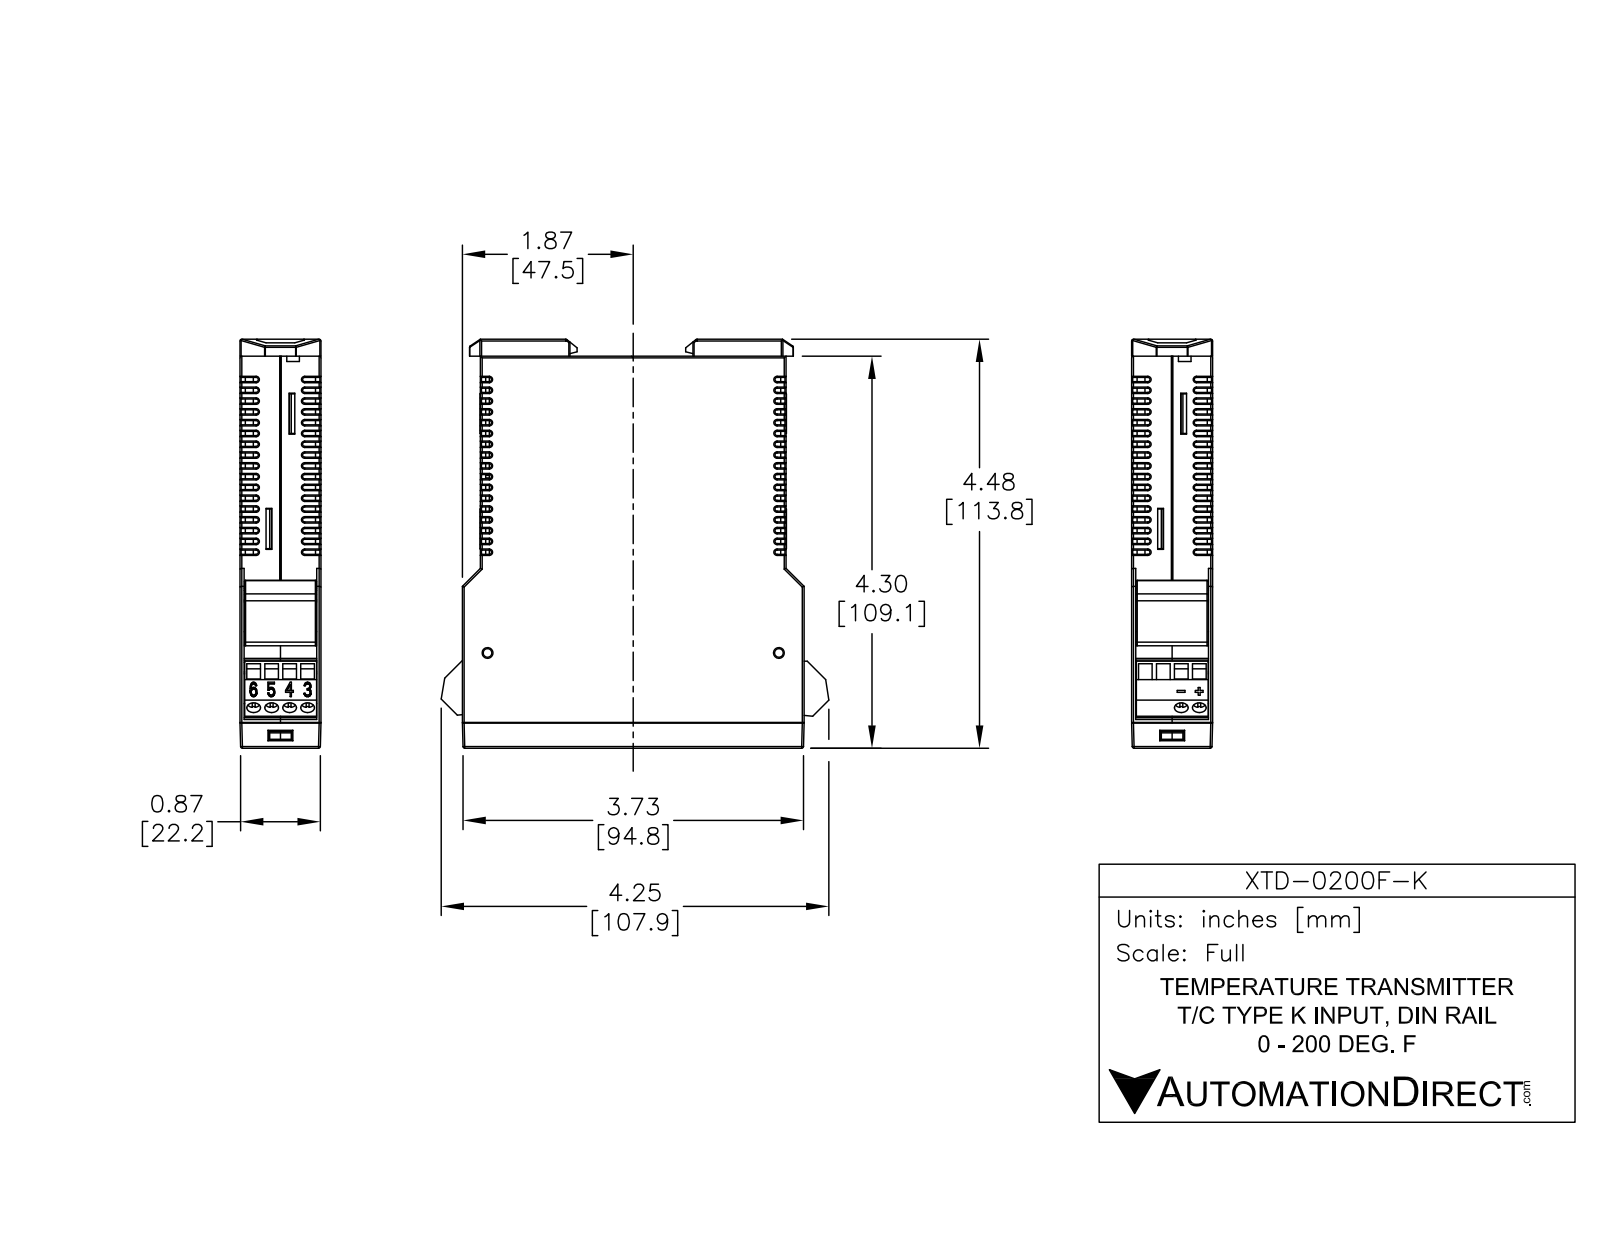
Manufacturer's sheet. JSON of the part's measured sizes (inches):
{"part_name": "XTD-0100F-J", "step_written_by": "SolidWorks 2017 (AUTOMOTIVE_DESIGN)", "units": "inches", "bodies": {"solids": 2, "faces": 7298, "planar": 5926, "cylindrical": 1015, "other": 357}, "overall_size": [4.48, 4.244, 0.886], "volume_in3": 2.838, "surface_area_in2": 110, "round_holes": [[0.059, 6], [0.118, 6], [0.15, 6], [0.094, 2], [0.157, 2], [0.079, 1], [0.138, 1]], "round_bosses_or_shafts": [[0.079, 2]], "partial_cylinders_radius": [[0.012, 190], [0.02, 80], [0.024, 68], [0.008, 48], [0.079, 11], [0.118, 5], [0.028, 4], [0.039, 4]], "face_to_face_distances": [0.059, 0.886, 0.039, 0.846, 0.02, 0.787, 0.827, 0.807, 0.045, 0.014], "hole_center_spacings": [0.197, 0.394, 0.591, 0.306, 0.357, 3.189]}
